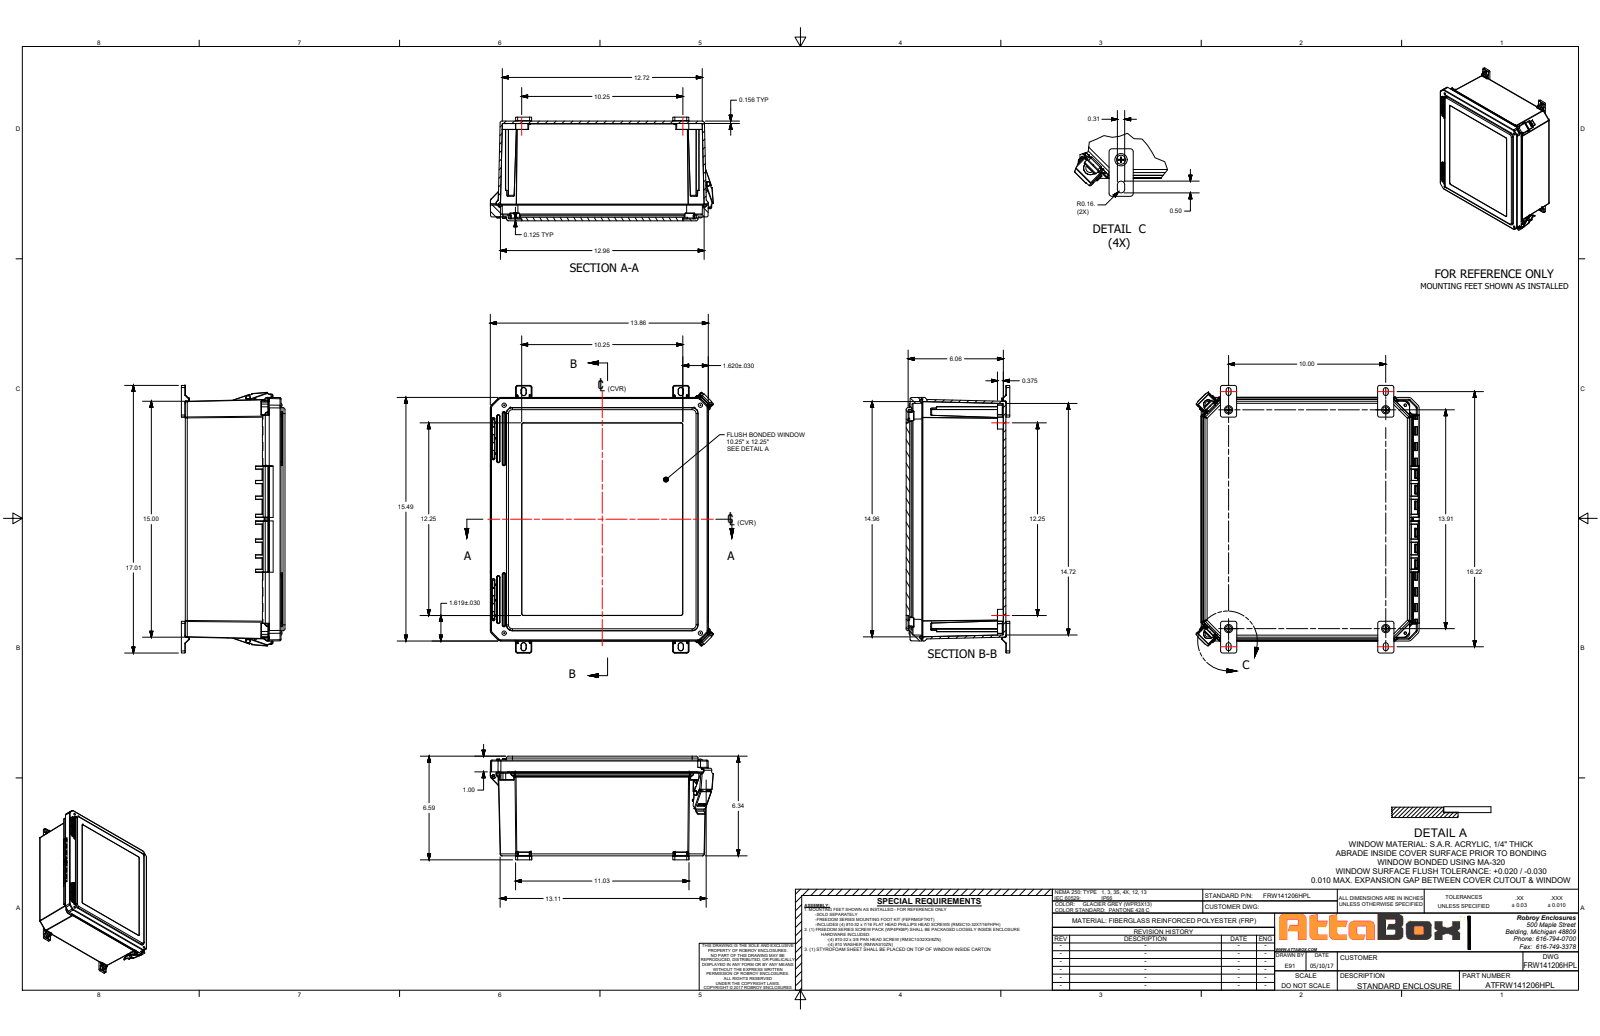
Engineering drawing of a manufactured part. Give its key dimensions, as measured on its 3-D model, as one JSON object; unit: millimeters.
{"part_name": "FRW141206HPL", "step_written_by": "SolidWorks 2021 (AUTOMOTIVE_DESIGN)", "units": "millimeters", "bodies": {"solids": 30, "faces": 2511, "planar": 810, "cylindrical": 1077, "other": 624}, "overall_size": [409.7, 360.2, 171.9], "volume_mm3": 2216000, "surface_area_mm2": 1081000, "round_holes": [[3.4, 8], [3.9, 8], [4, 8], [3.4, 4], [3.8, 4], [4, 4], [6.4, 4], [6.4, 4], [3.5, 3], [5.6, 2], [5.8, 2], [8, 2]], "round_bosses_or_shafts": [[6.9, 8], [22.1, 4], [7.6, 4], [6.7, 4], [5.3, 4], [3.4, 3], [11, 2], [3.4, 1]], "partial_cylinders_radius": [[0.3, 193], [0.1, 110], [0.8, 69], [0.5, 54], [1.5, 36], [2.3, 26], [3.2, 26], [0.8, 24]], "face_to_face_distances": [4, 157.1, 161, 5.7, 151.4, 155.3, 3.6, 3.2, 3.5, 3.5], "hole_center_spacings": [368, 340.8, 351.4, 40.2, 340.8, 362.1, 368, 445.8]}
